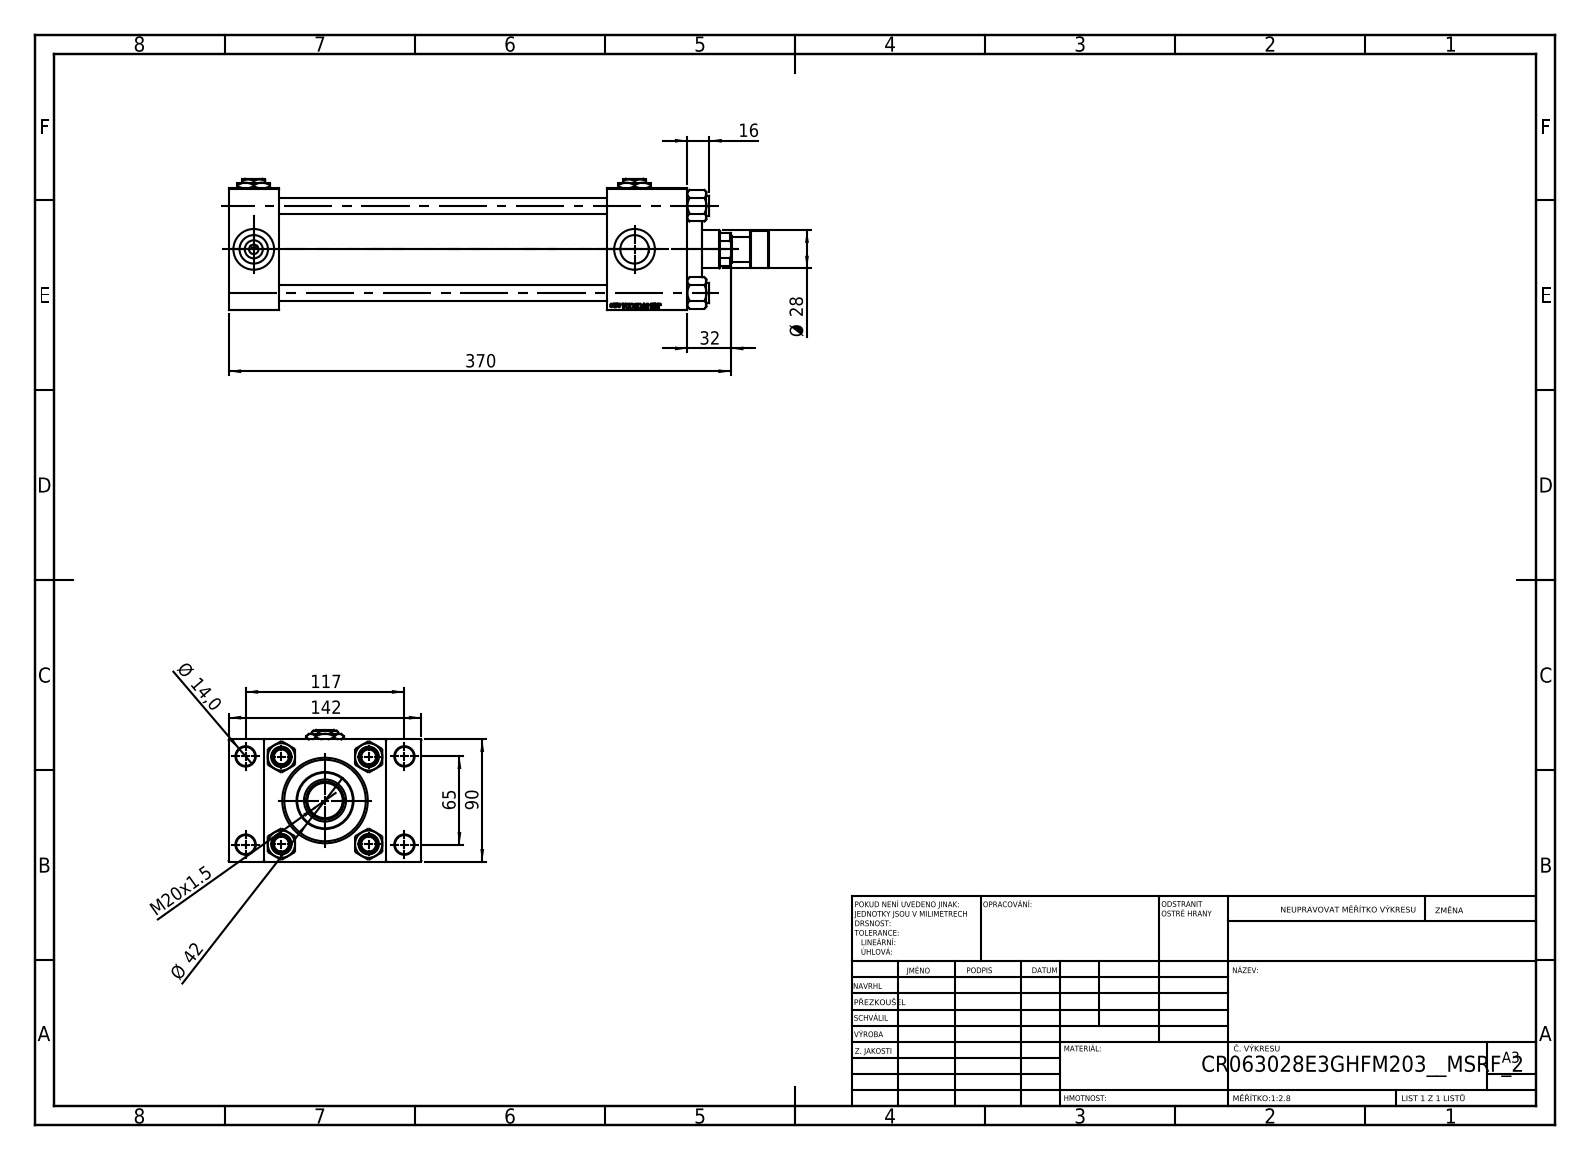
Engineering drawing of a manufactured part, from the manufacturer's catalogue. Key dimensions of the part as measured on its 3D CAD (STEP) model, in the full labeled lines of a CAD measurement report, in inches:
Part name (STEP PRODUCT): V215CR_TYCINKA_E; V215CR_VCP_E; V215CR_ROD_END_F; V215_VC_A (+3 more)
STEP written by: SolidWorks 2019 (CONFIG_CONTROL_DESIGN)
Units: inches
Bodies: 14 solids, 1251 faces (550 planar, 101 cylindrical, 600 other)
Overall size (bounding box): 15.669 × 5.591 × 3.819
Volume: 86.59 in³ · Surface area: 518.1 in²
Round holes (diameter × count): ⌀0.472 ×4, ⌀0.551 ×4, ⌀0.825 ×4, ⌀1.181 ×4, ⌀0.276 ×3, ⌀0.728 ×1, ⌀1.102 ×1, ⌀1.22 ×1, ⌀1.969 ×1, ⌀2.362 ×1, ⌀2.48 ×1
Round bosses / shafts (diameter × count): ⌀0.591 ×4, ⌀2.717 ×1, ⌀1.654 ×1, ⌀1.063 ×1, ⌀0.709 ×1
Main face-to-face distances: 3.543, 1.457, 13.307, 11.85, 1.024, 4.567, 2.323, 10.984, 9.528, 12.177
Hole centre spacings: 1.037, 1.79, 2.531, 2.635, 2.748, 3.569, 4.383, 2.559
